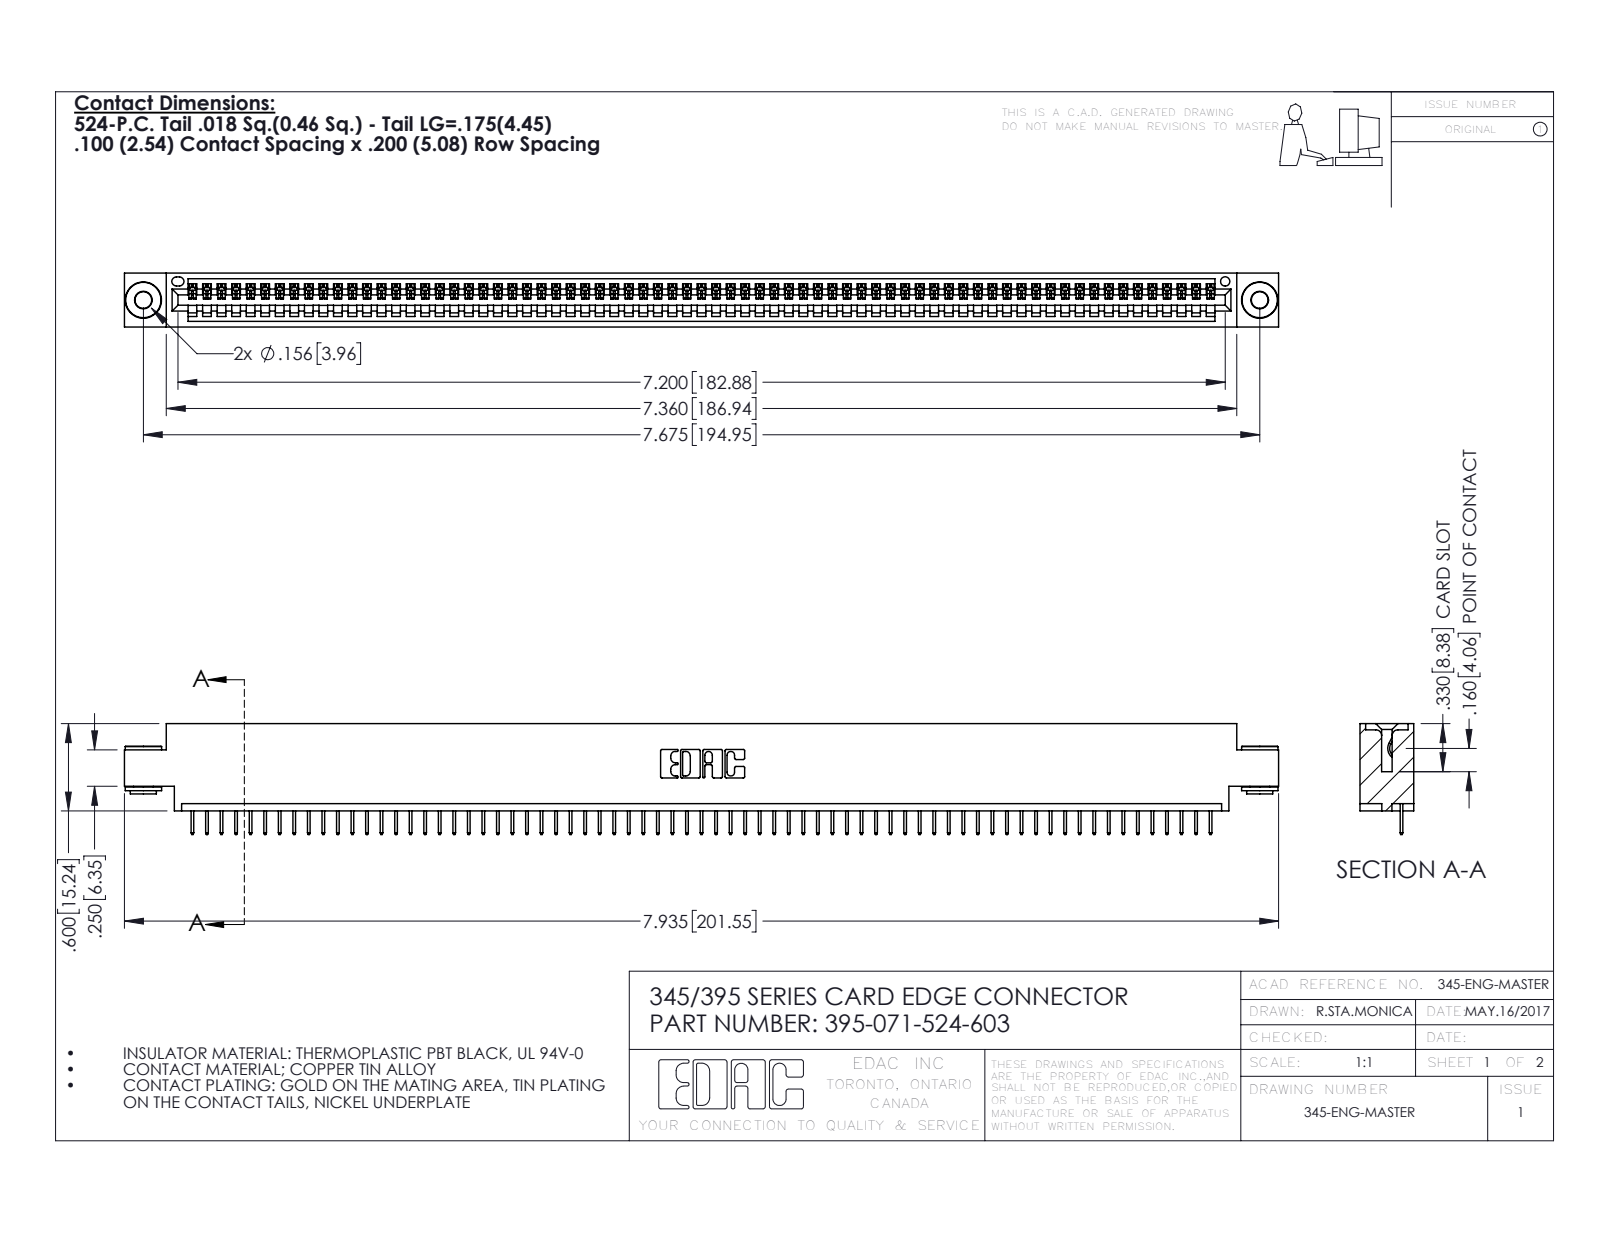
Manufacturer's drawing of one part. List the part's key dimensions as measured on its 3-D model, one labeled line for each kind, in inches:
Part name (STEP PRODUCT): 395-071-524-603; 345-250-002_345-250-002-102; 345 Part_0.170 Offset - 0.156 Dia-TH; 345-292-001_345-293-124
STEP written by: SolidWorks 2016 (CONFIG_CONTROL_DESIGN)
Units: inches
Bodies: 74 solids, 4570 faces (3360 planar, 1202 cylindrical, 8 other)
Overall size (bounding box): 7.935 × 0.762 × 0.37
Volume: 1.16 in³ · Surface area: 38.9 in²
Round holes (diameter × count): ⌀0.116 ×2, ⌀0.156 ×2, ⌀0.064 ×1
Round bosses / shafts (diameter × count): ⌀0.25 ×2, ⌀0.18 ×2, ⌀0.136 ×2
Partial cylindrical surfaces — rounded edges, fillets, slot ends (radius × count): R0.006 ×142, R0.01 ×22, R0.007 ×6, R0.031 ×6, R0.026 ×3, R0.031 ×2, R0.04 ×2, R0.014 ×1
Main face-to-face distances: 0.072, 0.298, 0.37, 0.2, 0.098, 0.272, 0.025, 0.225, 0.072, 0.175
Hole centre spacings: 0.27, 7.439, 7.675
